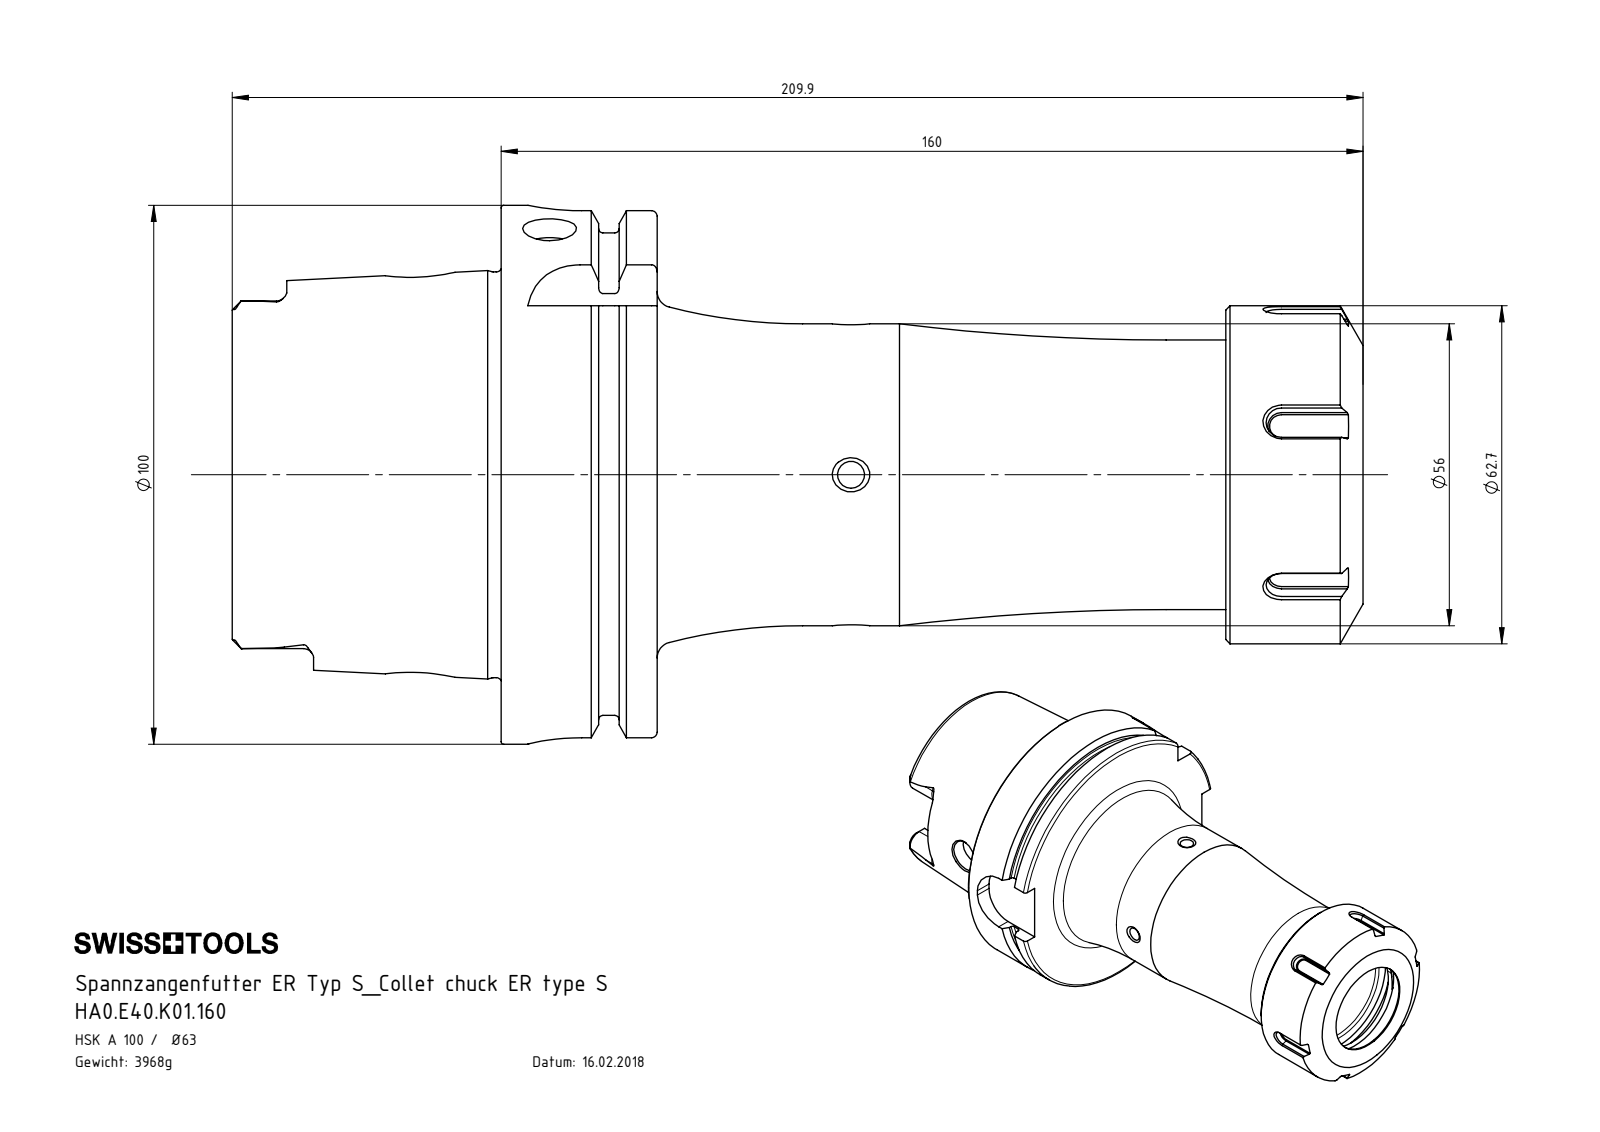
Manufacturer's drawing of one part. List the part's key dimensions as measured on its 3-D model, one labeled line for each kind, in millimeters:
Part name (STEP PRODUCT): E40-ER1.001.025; ERU-AN5.K01.020_A; HA0-E40.K01.160_C_Fertigbearbeitung; HA0.E40.K01.160
STEP written by: SolidWorks 2017 (CONFIG_CONTROL_DESIGN)
Units: millimetres
Bodies: 3 solids, 337 faces (126 planar, 81 cylindrical, 130 other)
Overall size (bounding box): 209.9 × 100 × 100
Volume: 505 461 mm³ · Surface area: 89 029 mm²
Round holes (diameter × count): ⌀10 ×3, ⌀5 ×2, ⌀12 ×2, ⌀6 ×1, ⌀11 ×1, ⌀22.5 ×1, ⌀26 ×1, ⌀30.5 ×1, ⌀33.5 ×1, ⌀48.5 ×1, ⌀50.5 ×1, ⌀53 ×1
Round bosses / shafts (diameter × count): ⌀100 ×1, ⌀91.95 ×1, ⌀75.26 ×1, ⌀62.7 ×1, ⌀56 ×1, ⌀50 ×1
Partial cylindrical surfaces — rounded edges, fillets, slot ends (radius × count): R1.9 ×6, R4.88 ×4, R10 ×4, R19.26 ×2
Main face-to-face distances: 28.95, 12.45, 16.5, 134.5, 122.05, 105.55, 160, 147.55, 131.05, 25.5
Hole centre spacings: 57.95, 79.95
